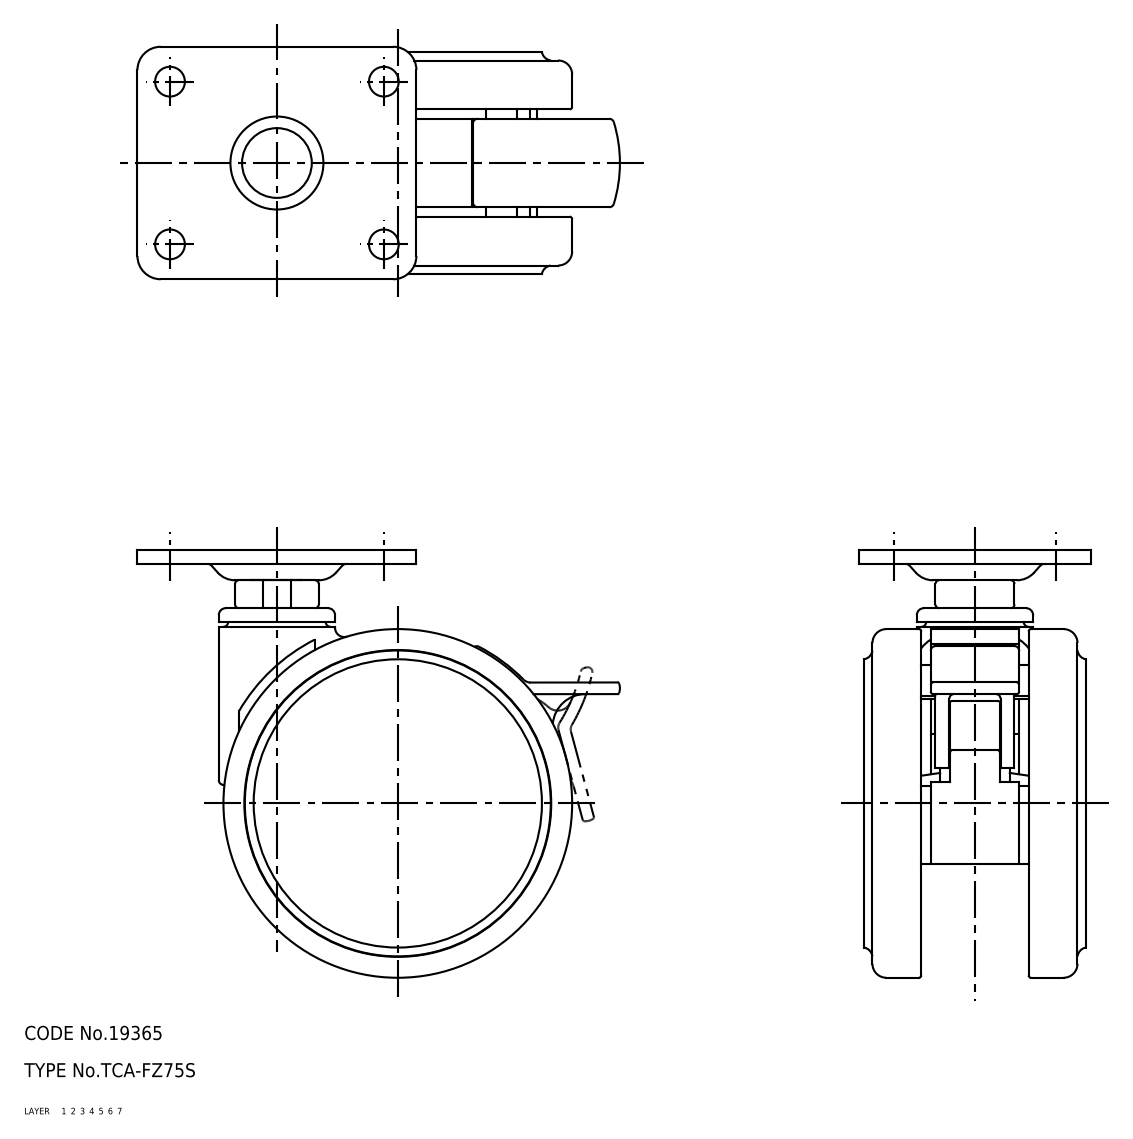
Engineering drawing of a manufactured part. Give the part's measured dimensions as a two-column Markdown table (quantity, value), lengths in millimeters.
| quantity | value |
| --- | --- |
| part name | TCA-FZ75S; caster |
| STEP written by | SolidWorks 2015 (AUTOMOTIVE_DESIGN) |
| units | millimeters |
| bodies | 2 solids, 2277 faces (509 planar, 998 cylindrical, 770 other) |
| overall size | 103.78 × 92 × 50 |
| volume | 126 228 mm³ |
| surface area | 76 557 mm² |
| round holes (diameter × count) | 6.4 × 4, 2.4 × 1, 3.6 × 1, 5.8 × 1, 6.5 × 1, 8 × 1, 8.1 × 1, 9 × 1, 10.2 × 1, 11 × 1, 16.2 × 1, 17 × 1 |
| round bosses / shafts (diameter × count) | 16 × 2, 14 × 2, 65.8 × 1, 54 × 1, 26 × 1, 25 × 1, 10 × 1, 8.1 × 1 |
| partial cylindrical surfaces (radius × count) | 1 × 175, 0.5 × 158, 0.3 × 153, 0.2 × 18, 2 × 13, 1.5 × 7, 5 × 5, 0.7 × 2 |
| main face-to-face distances | 1.5, 46.2, 3.3, 1.8, 44.4, 42.9, 32.1, 9, 12.3, 35.4 |
| hole center spacings | 28.9, 35, 46, 57.8, 30 |
